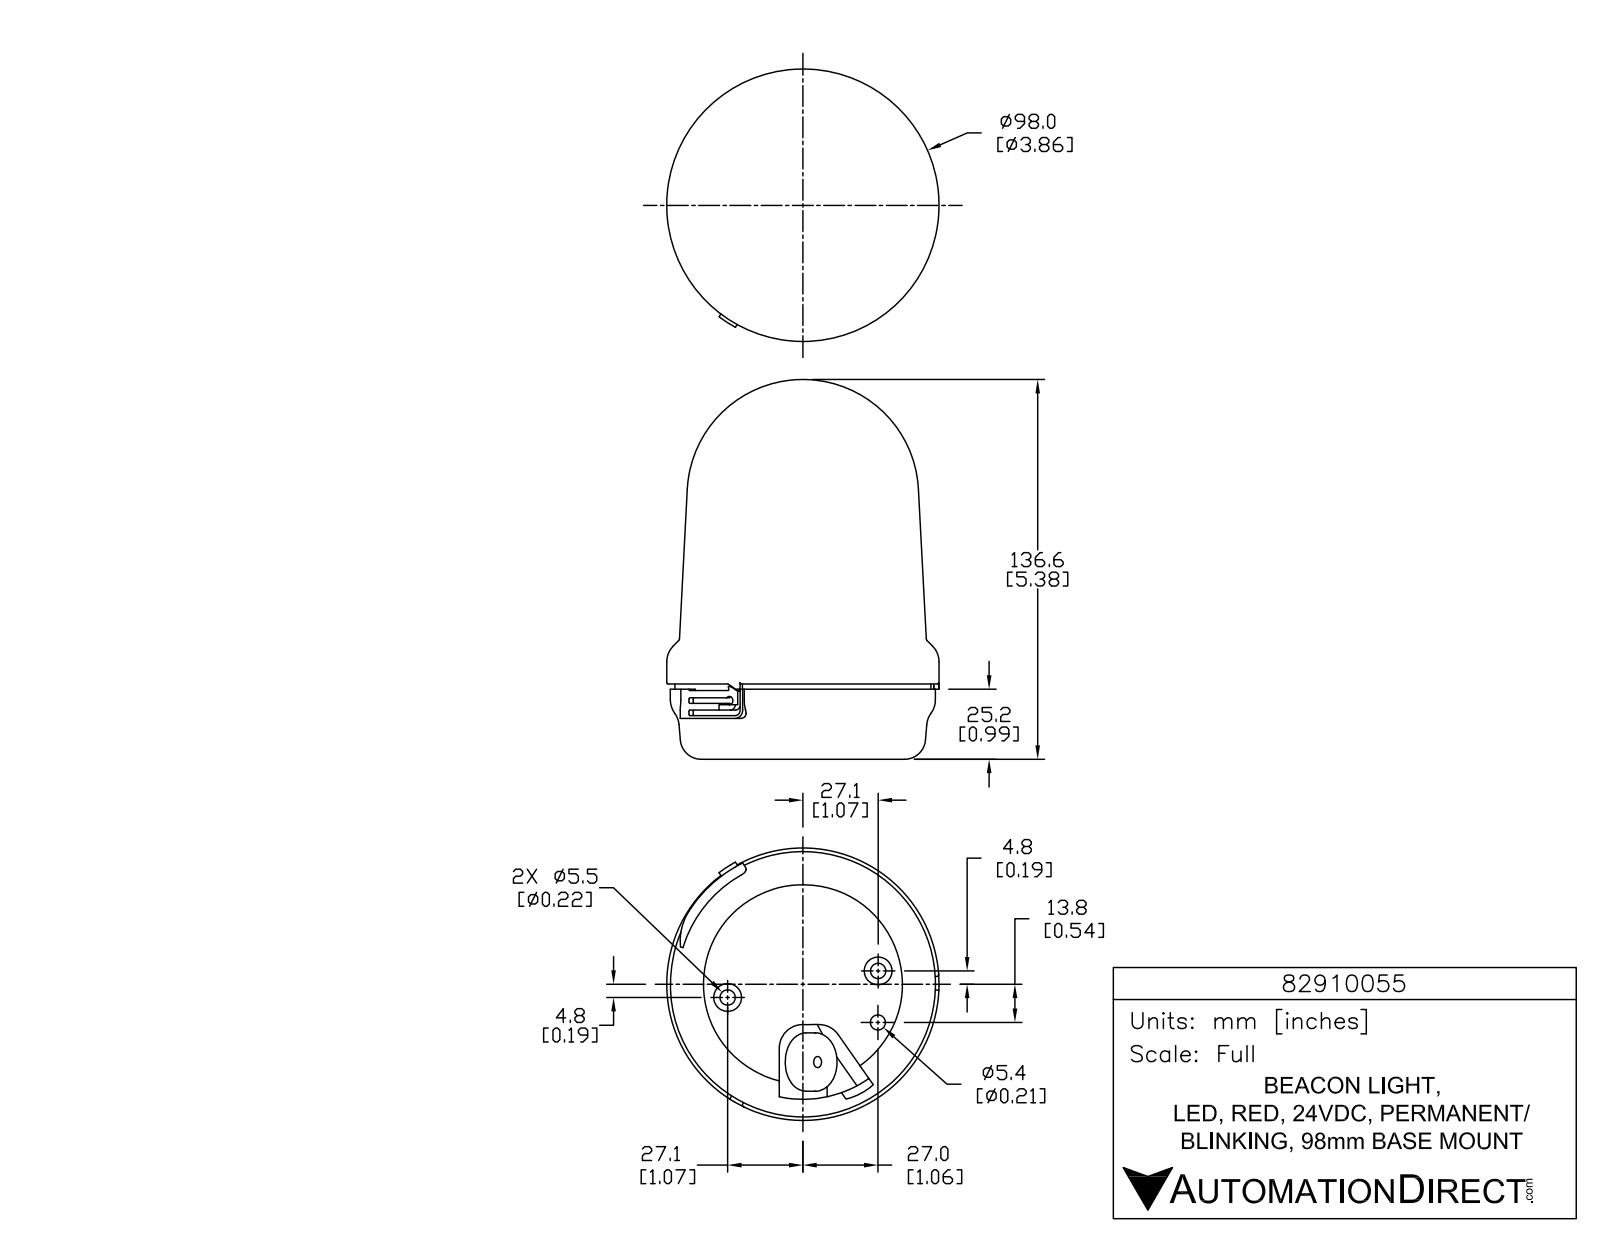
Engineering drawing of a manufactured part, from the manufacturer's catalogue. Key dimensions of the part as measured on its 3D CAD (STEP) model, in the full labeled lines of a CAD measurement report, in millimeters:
Part name (STEP PRODUCT): 82910055
STEP written by: SolidWorks 2015 (AUTOMOTIVE_DESIGN)
Units: millimetres
Bodies: 1 solid, 872 faces (566 planar, 204 cylindrical, 102 other)
Overall size (bounding box): 136.6 × 98 × 98
Volume: 732 300 mm³ · Surface area: 47 520 mm²
Round holes (diameter × count): ⌀1.5 ×3, ⌀5.5 ×2, ⌀4 ×1, ⌀5.4 ×1, ⌀71.6 ×1
Round bosses / shafts (diameter × count): ⌀8.6 ×3, ⌀2.1 ×3, ⌀10 ×2, ⌀98 ×1, ⌀95.4 ×1, ⌀92.1 ×1, ⌀21 ×1
Partial cylindrical surfaces — rounded edges, fillets, slot ends (radius × count): R0.1 ×9, R0.1 ×6, R0.3 ×6, R0.3 ×6, R0.3 ×6, R5 ×6, R0.5 ×5, R1 ×4
Main face-to-face distances: 26.5, 24.7, 1.9, 0.5, 25.2, 27.1, 6, 14.7, 14.2, 10.5
Hole centre spacings: 27.5, 18.5, 30.3, 54.8, 55
